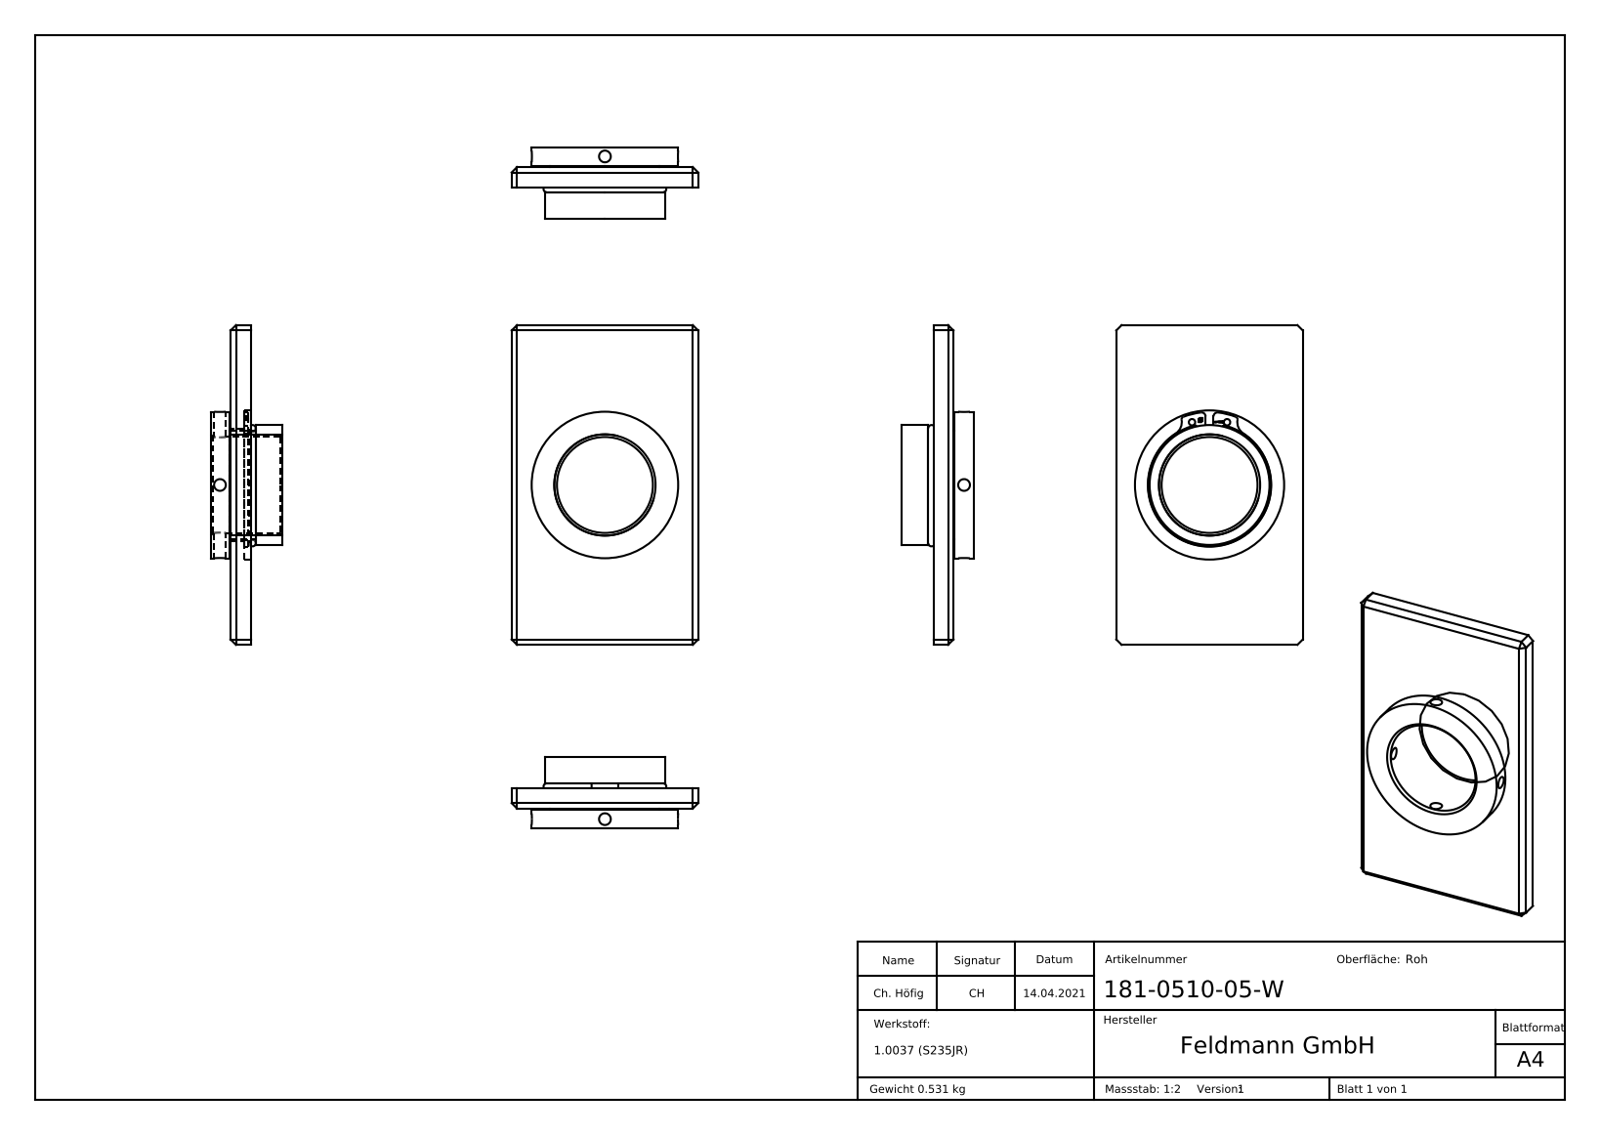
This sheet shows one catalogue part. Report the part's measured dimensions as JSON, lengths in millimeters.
{"part_name": "181-0510-05-W", "step_written_by": "SolidWorks 2018 (CONFIG_CONTROL_DESIGN)", "units": "millimeters", "bodies": {"solids": 4, "faces": 364, "planar": 188, "cylindrical": 40, "other": 136}, "overall_size": [120, 70, 27], "volume_mm3": 68038, "surface_area_mm2": 30281, "round_holes": [[2.4, 2], [4.4, 2], [36, 1], [41.1, 1], [42, 1], [56, 1]], "round_bosses_or_shafts": [[55, 1], [46.3, 1], [45, 1], [41, 1]], "partial_cylinders_radius": [[1, 2], [1.5, 2], [5, 2], [27.4, 1]], "face_to_face_distances": [7.5, 15, 5.1, 2.4, 12.6, 8, 5.6, 0.5, 7, 70], "hole_center_spacings": [24.45, 13.16]}
